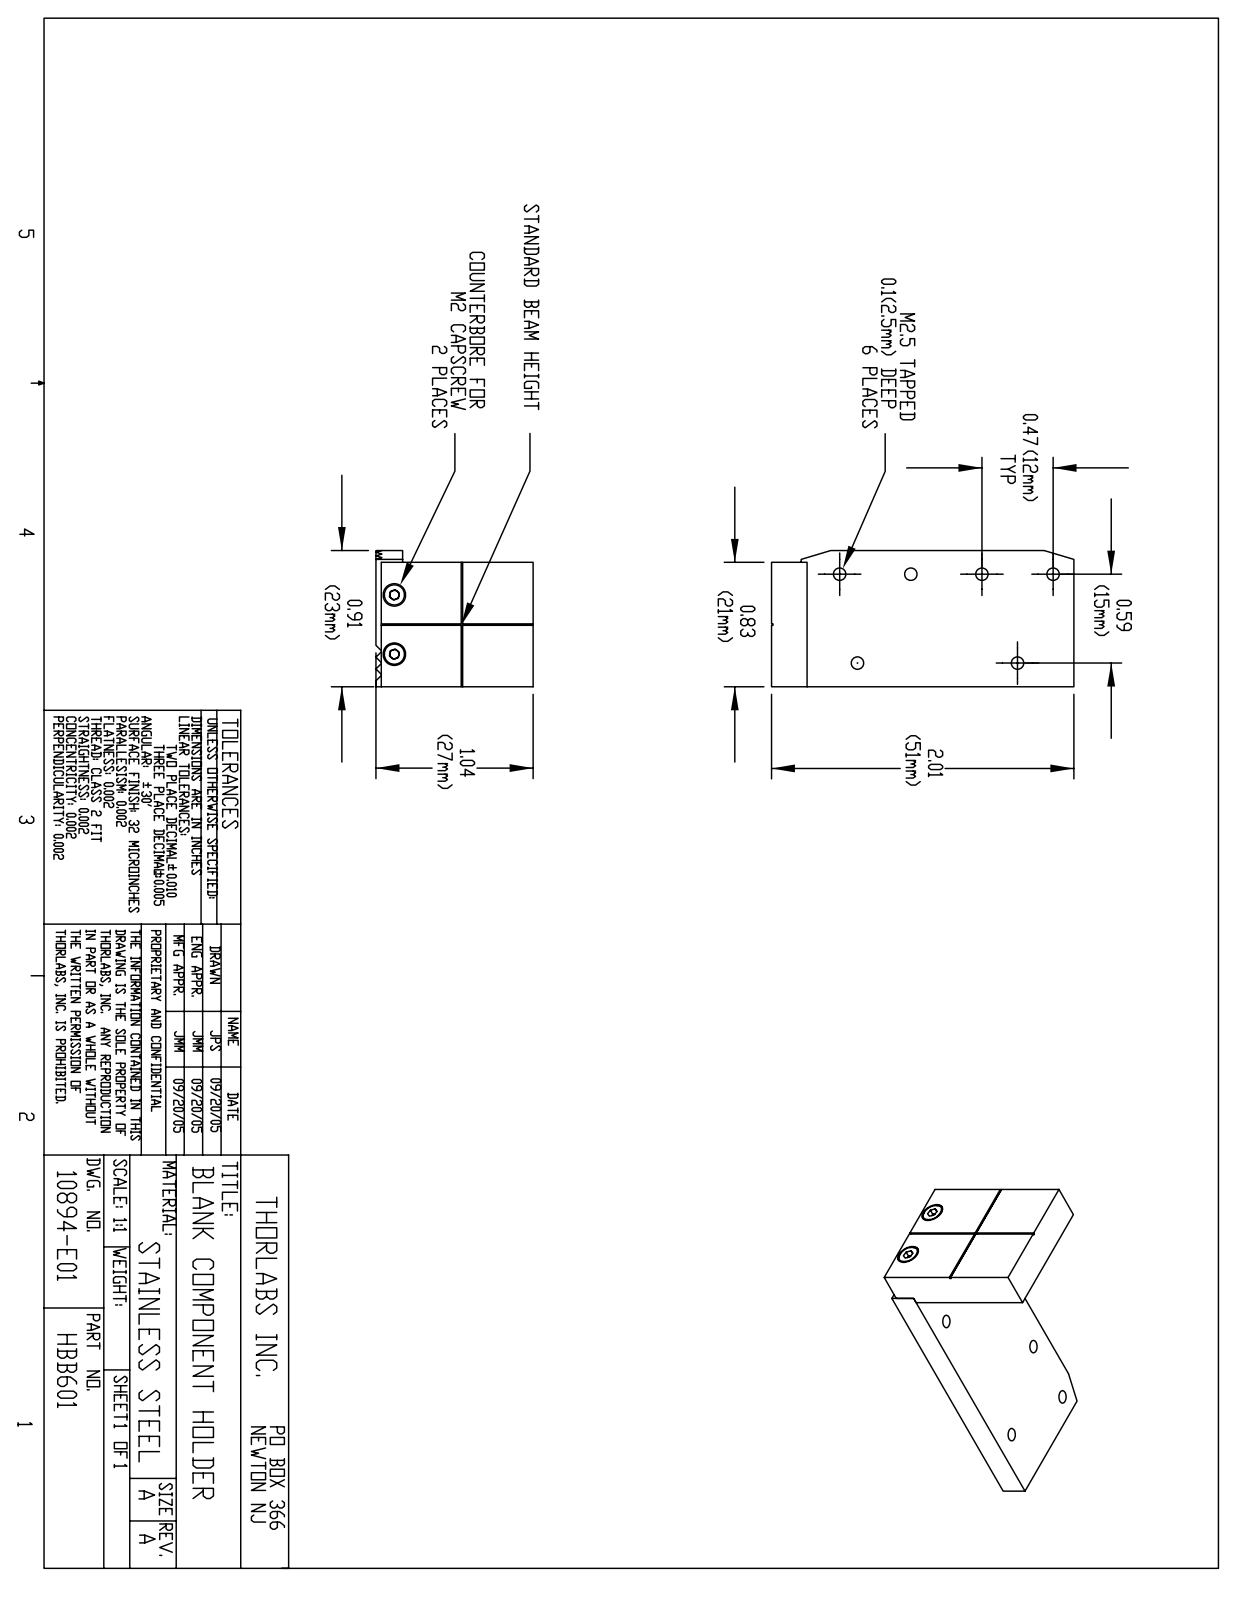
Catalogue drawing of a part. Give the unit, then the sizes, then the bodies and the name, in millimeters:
Units: millimetres
Overall size (bounding box): 51 × 26.5 × 23
Round holes (diameter × count): ⌀2.1 ×6, ⌀1.6 ×2, ⌀3.8 ×2
Main face-to-face distances: 2.8, 1.4, 7.1, 6, 4.2, 1.4, 9.9, 14.1, 5.7, 11.3
Hole centre spacings: 12, 16.2, 24, 10, 15.3, 17.5, 23.4, 25.8
Bodies: 0 solids, 177 faces (126 planar, 20 cylindrical, 31 other)
Part name (STEP PRODUCT): 10894-E0W
STEP written by: SolidWorks 2007 (AUTOMOTIVE_DESIGN)
